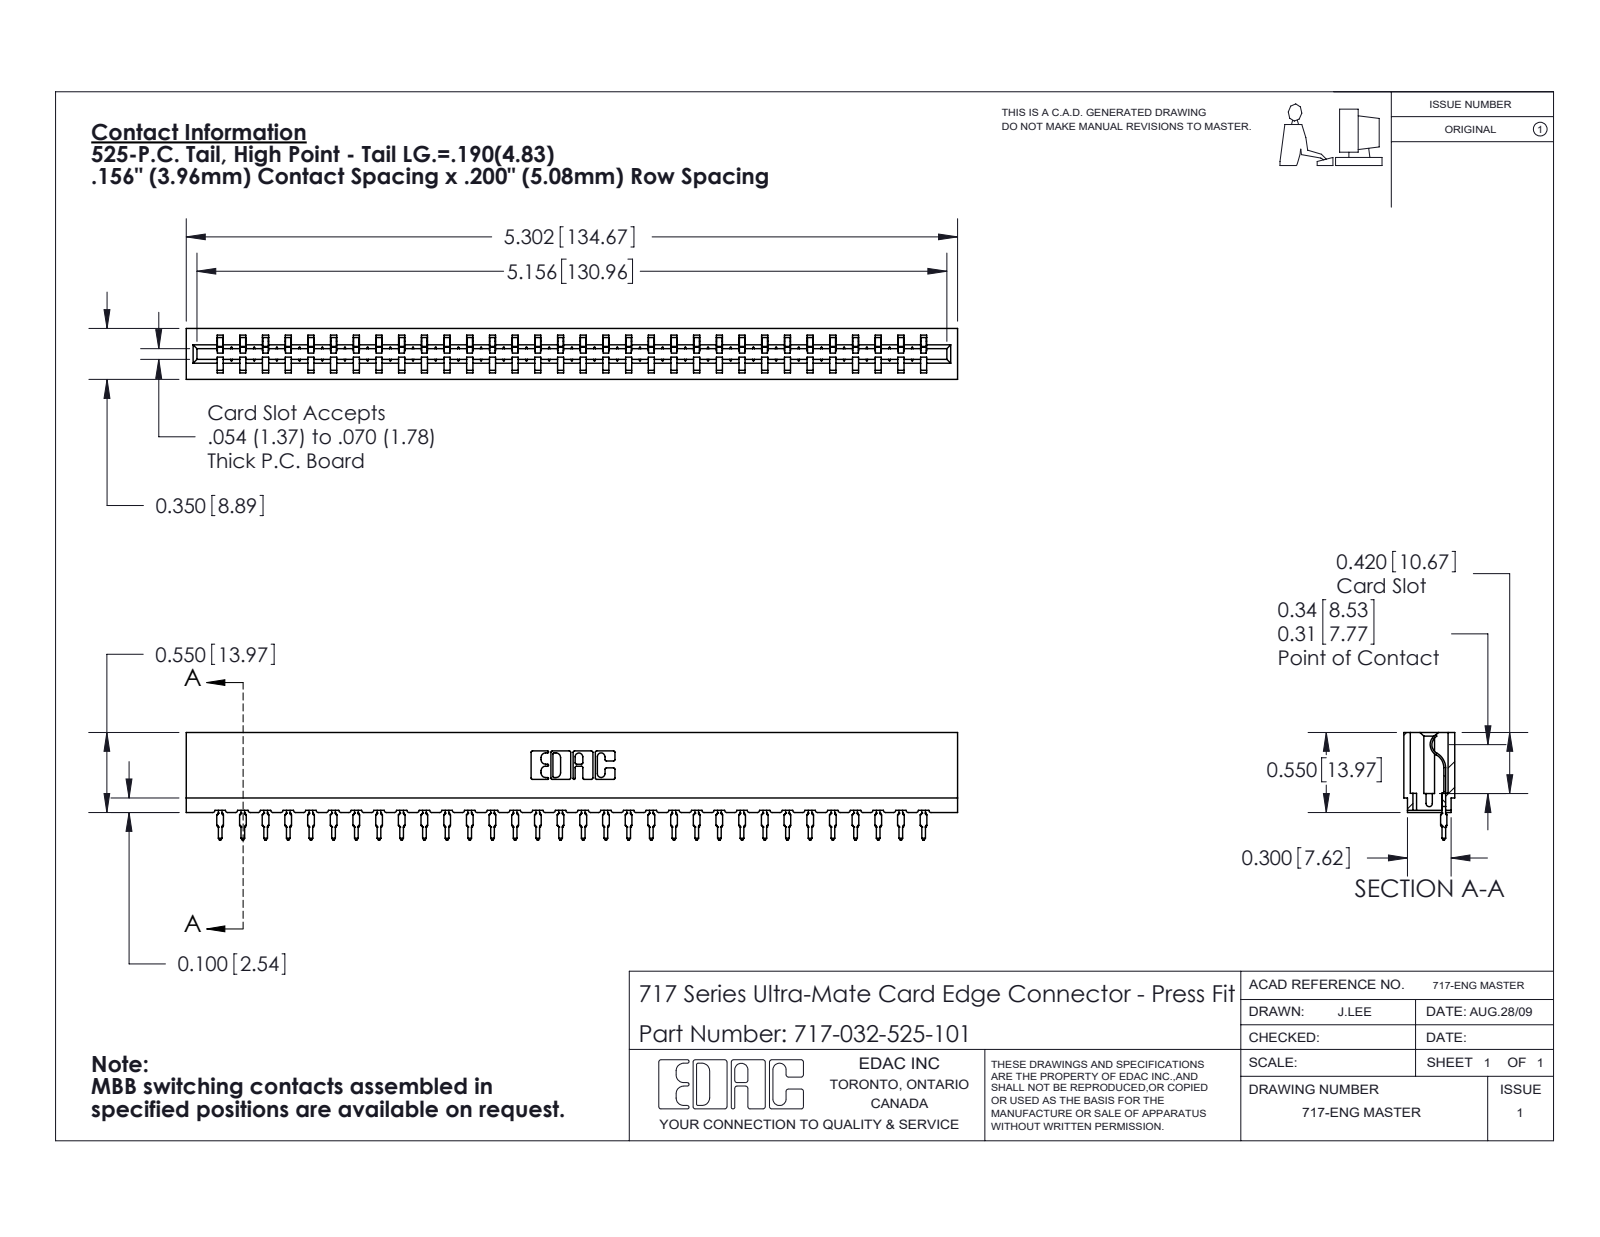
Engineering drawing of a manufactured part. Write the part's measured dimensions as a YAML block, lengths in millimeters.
part_name: "745-292-001_525; 717 Part_Insulator Option - 06; 717-032-525-101"
step_written_by: "SolidWorks 2020 (CONFIG_CONTROL_DESIGN)"
units: millimeters
bodies: {solids: 33, faces: 3710, planar: 2230, cylindrical: 648, other: 832}
overall_size: [134.7, 18.8, 8.9]
volume: 11400
surface_area: 15790
partial_cylinders:
  - {radius: 0.4, count: 64}
  - {radius: 0.5, count: 64}
  - {radius: 0.3, count: 22}
  - {radius: 0.2, count: 6}
  - {radius: 0.8, count: 6}
  - {radius: 0.1, count: 4}
  - {radius: 0.3, count: 4}
  - {radius: 0.7, count: 3}
face_to_face_distances: [5.4, 3.5, 8.9, 1.9, 1.1, 7.7, 2.4, 4.2, 4, 0.6]
